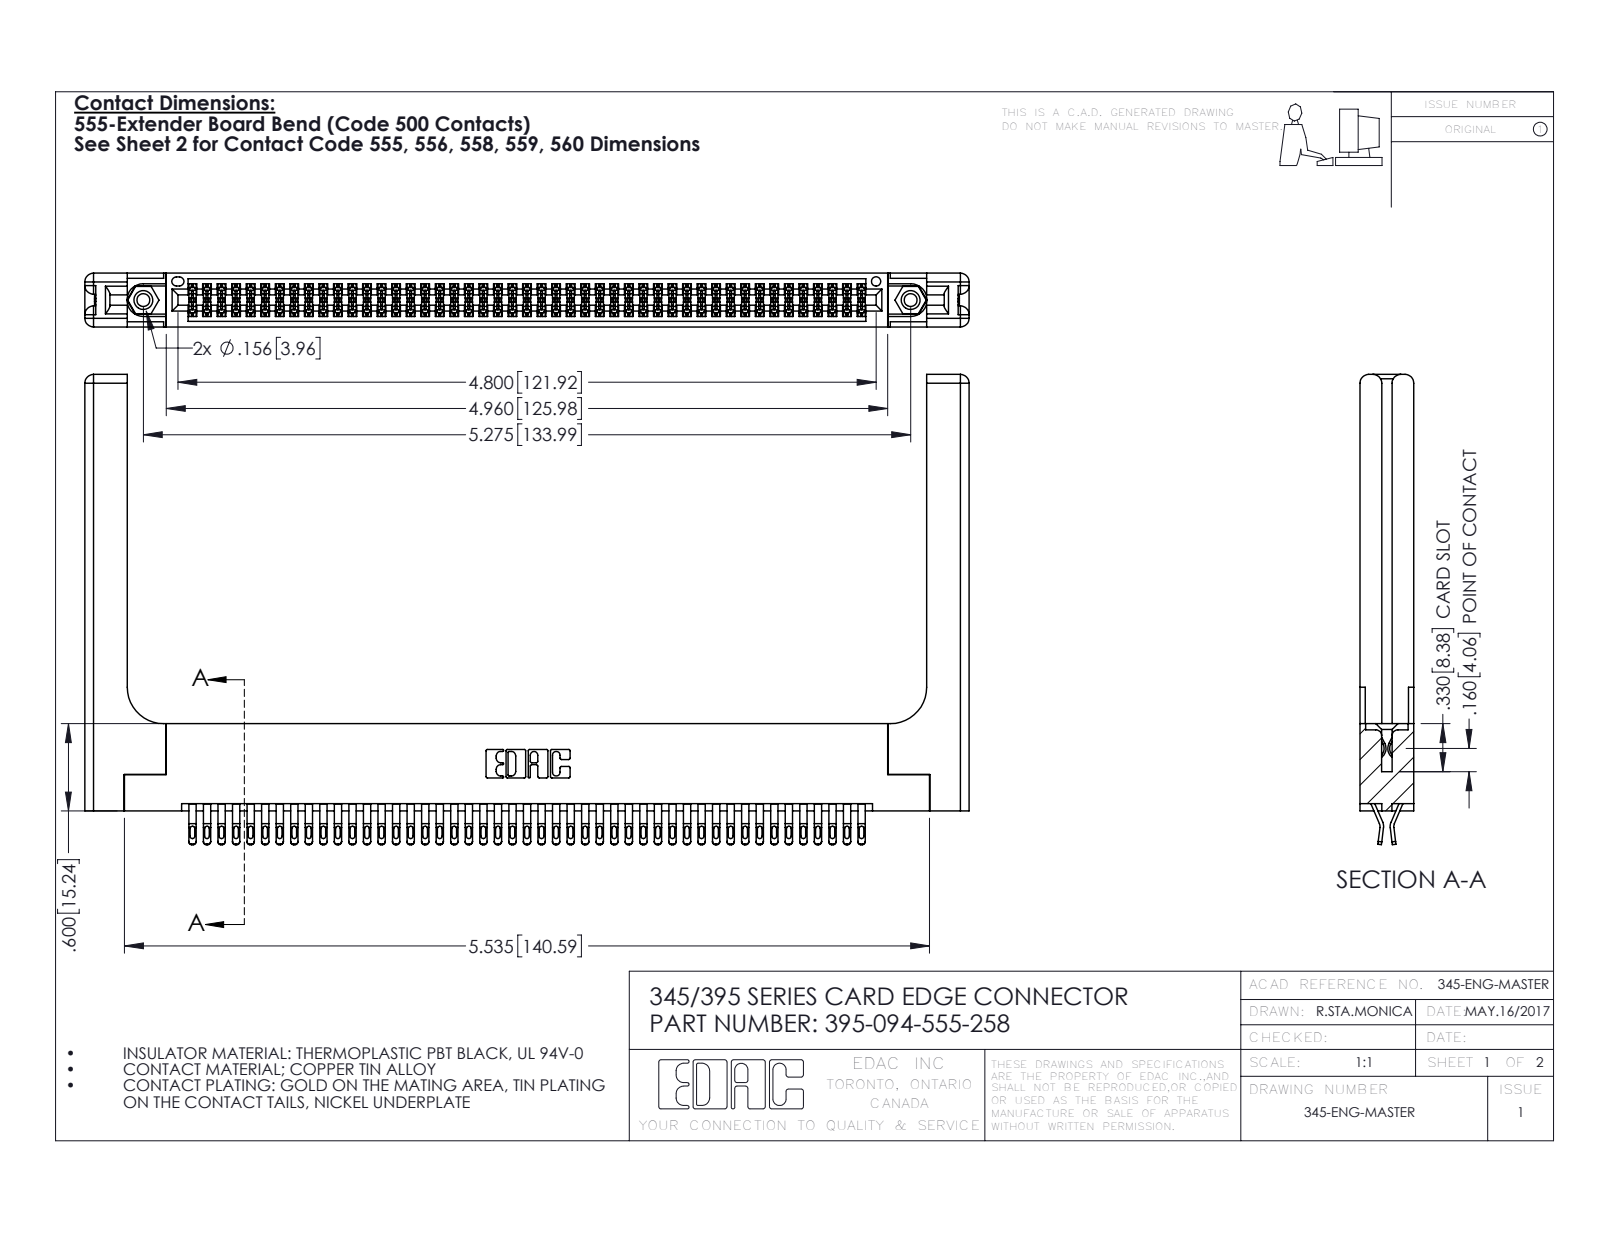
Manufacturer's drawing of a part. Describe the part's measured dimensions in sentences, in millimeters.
The part is named "345 Part_Flush Mounting Lugs - 0.156 Dia-TH; 345-250-001_345-250-001-102; 395-094-555-258; 345-220-058_345-220-058 (+1 more)". Its 3-D file was written by "SolidWorks 2016 (CONFIG_CONTROL_DESIGN)". It is 99 solids with 5646 faces: 3142 planar, 2444 cylindrical and 60 other. Overall it measures 154.4 by 82.1 by 9.4 millimeters. Its volume is 23 790 cubic millimeters and its surface area 28 750 square millimeters. Round holes: 2 of diameter 2.3, 2 of diameter 3.2, 2 of diameter 4, 1 of diameter 1.6. Round bosses or shafts: 2 of diameter 3.9. Partial cylindrical surfaces (rounded edges, fillets, slot ends): 235 of radius 0.4, 188 of radius 0.5, 141 of radius 0.2, 22 of radius 0.3, 16 of radius 1.5, 6 of radius 0.2, 6 of radius 0.8, 3 of radius 0.7. The main face-to-face distances are 1.8, 9.4, 7.6, 0.6, 5.1, 2.5, 6.9, 5.7, 3.8, 3.8. The hole center spacings are 6.9, 128, 134.
